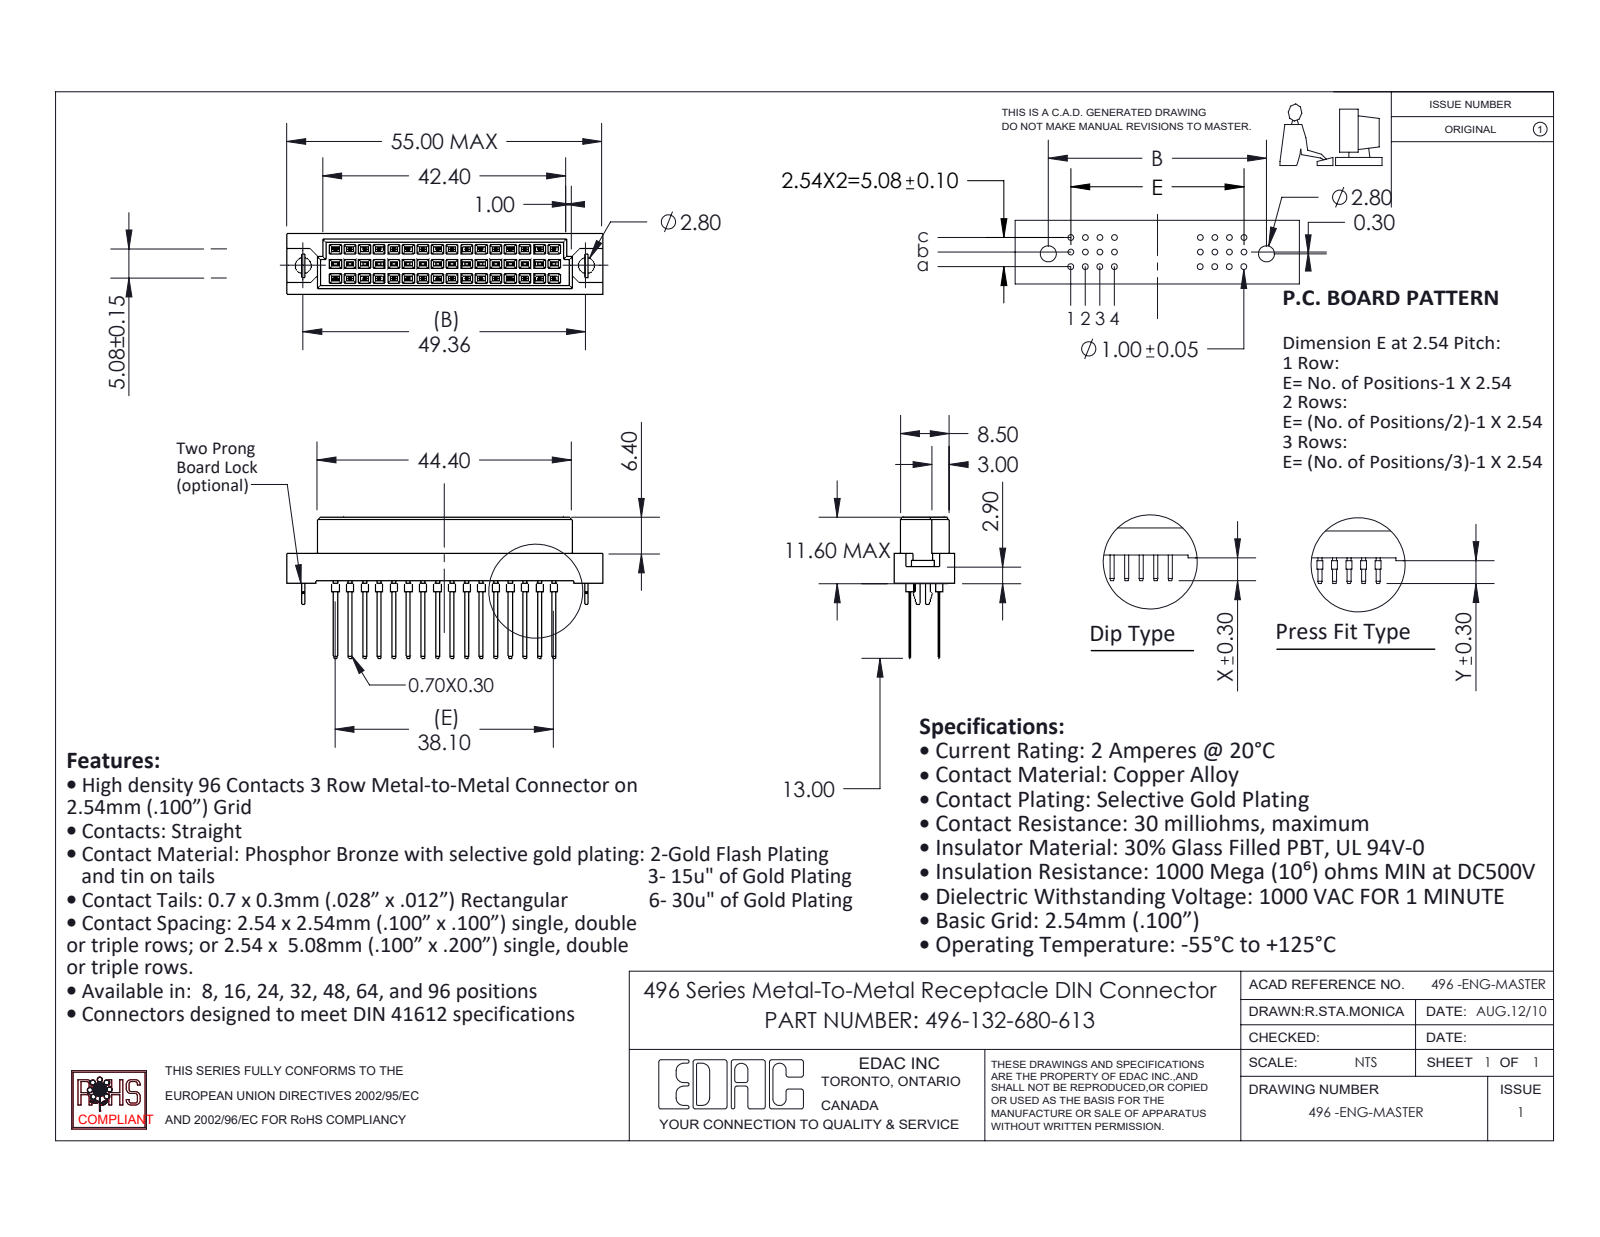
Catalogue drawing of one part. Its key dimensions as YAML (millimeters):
part_name: "496-132-680-613; 496-290_80; 496 Part_48; 496 Bore-lock"
step_written_by: "SolidWorks 2020 (CONFIG_CONTROL_DESIGN)"
units: millimeters
bodies: {solids: 35, faces: 1278, planar: 1208, cylindrical: 70, other: 0}
overall_size: [55, 24.6, 10.6]
volume: 4755
surface_area: 5530
round_holes:
  - {diameter: 2.8, count: 2}
round_bosses_or_shafts:
  - {diameter: 1, count: 32}
partial_cylinders:
  - {radius: 0.53, count: 1}
face_to_face_distances: [2.54, 5.08, 1.05, 9.55, 1.56, 1.86, 2.61, 2.91, 7.69, 7.99]
hole_center_spacings: [49.36]
